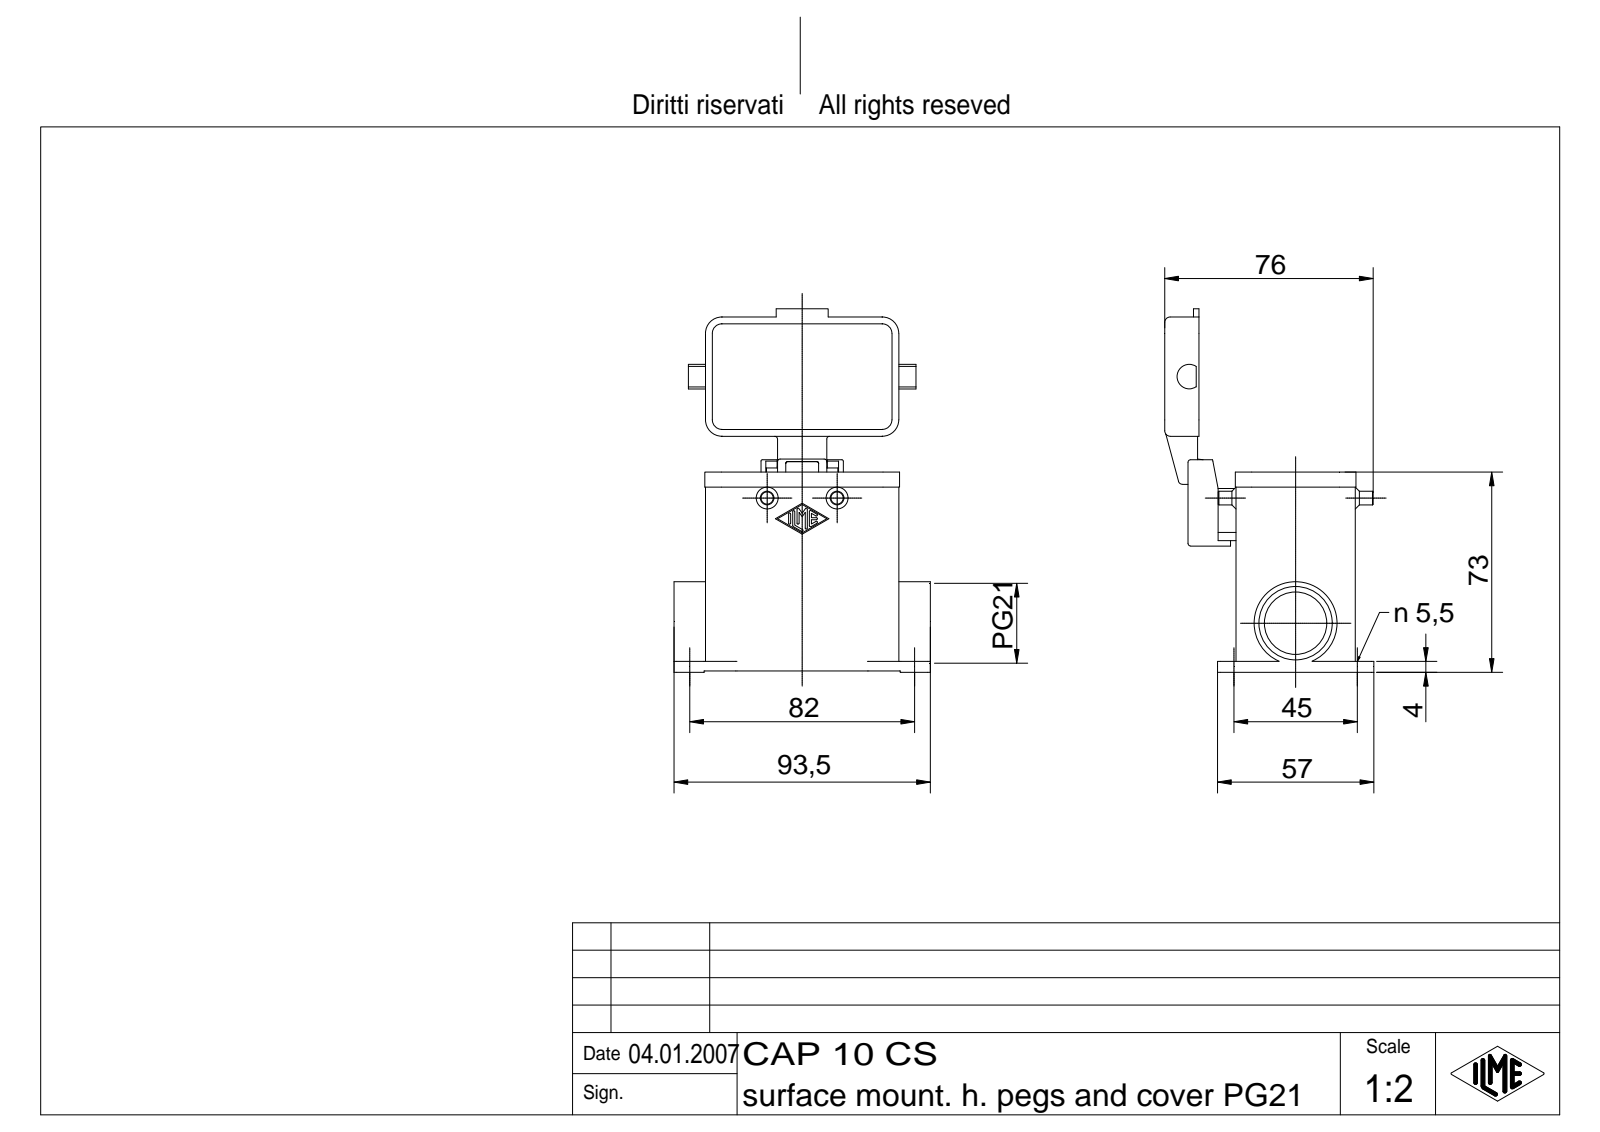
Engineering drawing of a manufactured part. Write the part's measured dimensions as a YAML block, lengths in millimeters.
part_name: "CAP 10 CS"
step_written_by: "Autodesk Inventor 7 (AUTOMOTIVE_DESIGN)"
units: millimeters
bodies: {solids: 2, faces: 475, planar: 175, cylindrical: 179, other: 121}
overall_size: [132.5, 93.5, 76.25]
volume: 111104
surface_area: 59884
round_holes:
  - {diameter: 5.5, count: 4}
  - {diameter: 4, count: 1}
  - {diameter: 5, count: 1}
  - {diameter: 22.78, count: 1}
  - {diameter: 26.78, count: 1}
round_bosses_or_shafts:
  - {diameter: 5, count: 2}
  - {diameter: 3, count: 2}
  - {diameter: 30.28, count: 1}
  - {diameter: 7, count: 1}
  - {diameter: 4, count: 1}
partial_cylinders:
  - {radius: 1, count: 26}
  - {radius: 0.38, count: 14}
  - {radius: 6, count: 12}
  - {radius: 0.5, count: 9}
  - {radius: 0.7, count: 8}
  - {radius: 2, count: 8}
  - {radius: 3, count: 4}
  - {radius: 3.5, count: 4}
face_to_face_distances: [3, 40.5, 3.5, 43.5, 37.5, 22.5, 66.5, 63, 66, 69.5]
hole_center_spacings: [45, 82, 93.54]
